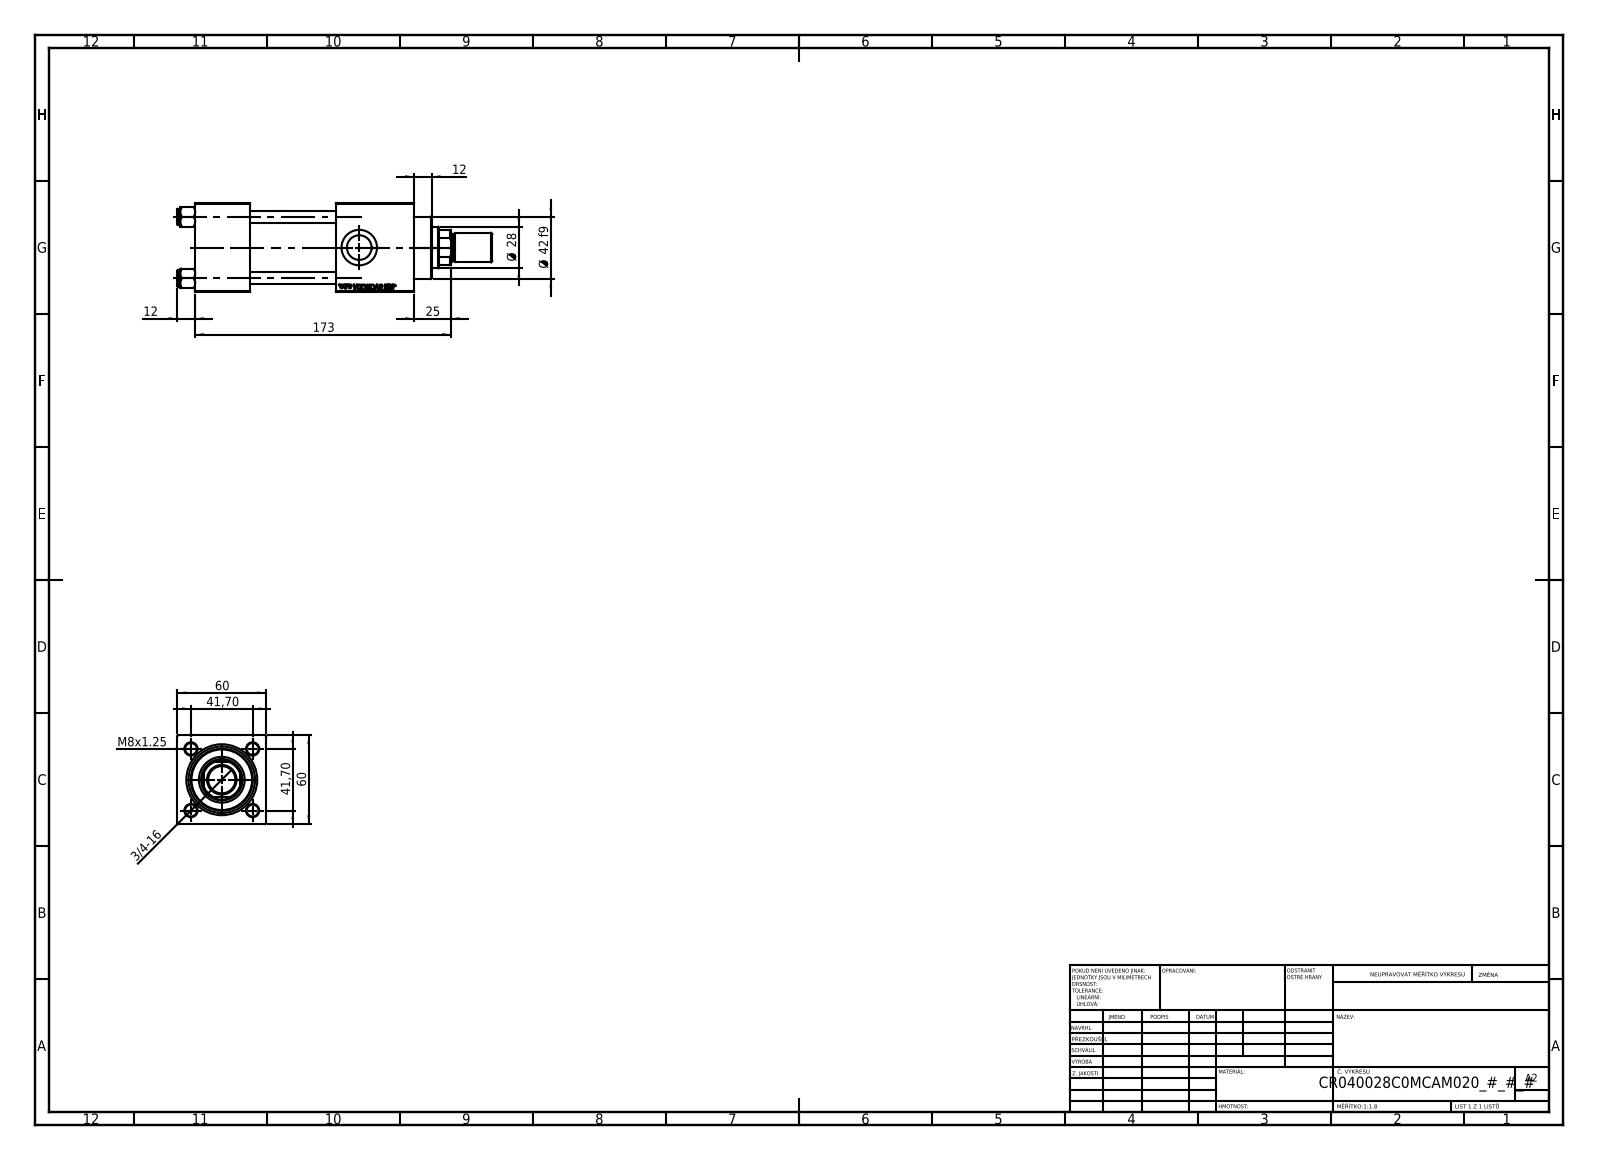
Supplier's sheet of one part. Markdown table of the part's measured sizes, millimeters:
| quantity | value |
| --- | --- |
| part name | NUT_M5_C; V215CR_C_Body; V215_VC_A; ROD_END_AH (+2 more) |
| STEP written by | SolidWorks 2019 (CONFIG_CONTROL_DESIGN) |
| units | millimeters |
| bodies | 12 solids, 1163 faces (530 planar, 91 cylindrical, 542 other) |
| overall size | 213 × 60 × 60 |
| volume | 432 757 mm³ |
| surface area | 113 865 mm² |
| round holes (diameter × count) | 8 × 4, 7 × 2, 16.66 × 2, 24 × 2, 18.5 × 1, 28 × 1, 31 × 1, 40 × 1, 45 × 1 |
| round bosses / shafts (diameter × count) | 11 × 4, 46 × 1, 42 × 1, 20 × 1, 18 × 1 |
| partial cylindrical surfaces (radius × count) | 13.5 × 1 |
| main face-to-face distances | 60, 37, 58, 53, 95, 119.3, 82.3, 24.3, 148, 111 |
| hole center spacings | 29.49, 41.7, 58.97 |
